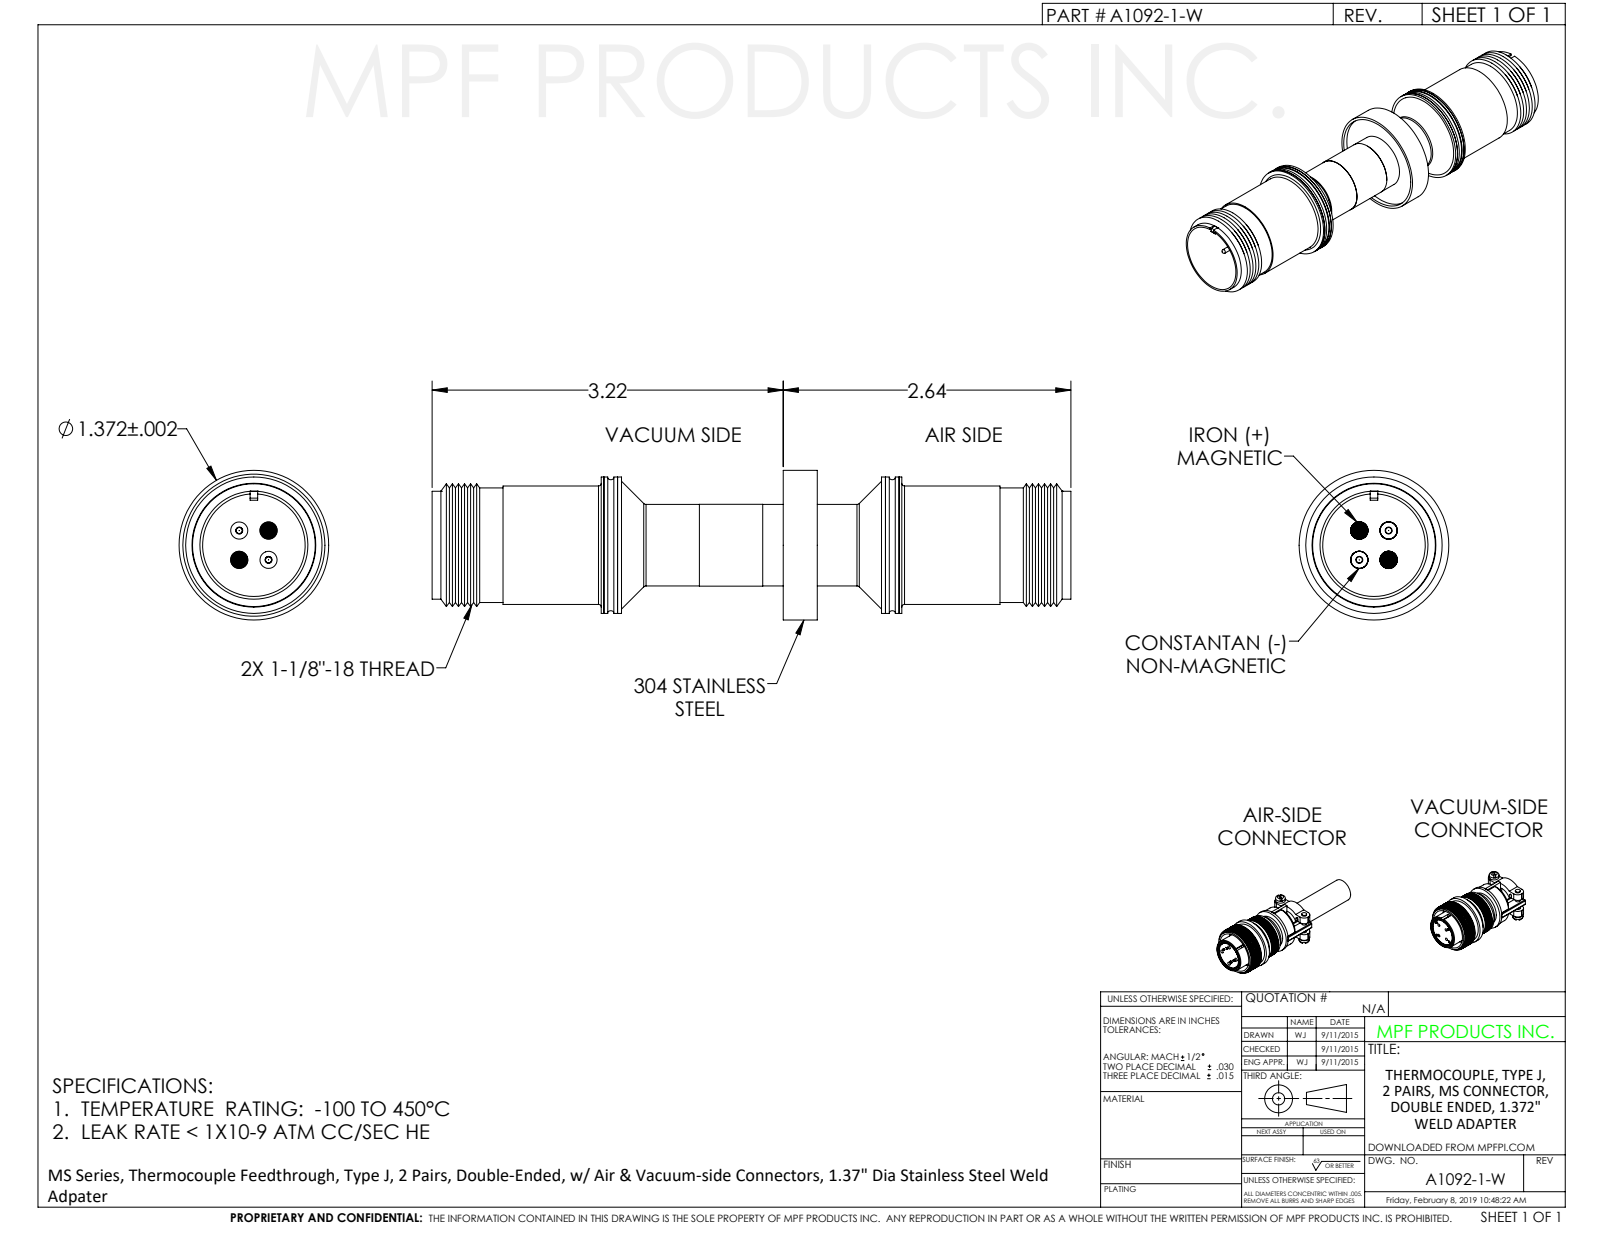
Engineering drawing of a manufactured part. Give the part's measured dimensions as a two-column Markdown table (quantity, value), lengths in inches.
| quantity | value |
| --- | --- |
| part name | A1092-1-W |
| STEP written by | SolidWorks 2012 (CONFIG_CONTROL_DESIGN) |
| units | inches |
| bodies | 1 solid, 357 faces (95 planar, 176 cylindrical, 86 other) |
| overall size | 5.855 × 1.372 × 1.372 |
| volume | 1.515 in³ |
| surface area | 58.04 in² |
| round holes (diameter × count) | 0.94 × 2, 0.96 × 2, 0.97 × 2, 1.035 × 2, 0.625 × 1, 0.675 × 1, 0.682 × 1, 0.751 × 1, 1.302 × 1 |
| round bosses / shafts (diameter × count) | 0.171 × 8, 0.187 × 4, 0.056 × 4, 1.25 × 2, 1.085 × 2, 1.05 × 2, 1.02 × 2, 1 × 2 |
| main face-to-face distances | 0.05, 3.515, 0.252, 1.432, 1.18, 2.133, 2.385, 3.565, 1.382, 1.13 |
| hole center spacings | 0.19, 0.269, 0.38, 0.039, 0.19, 0.239, 0.269, 0.295 |
